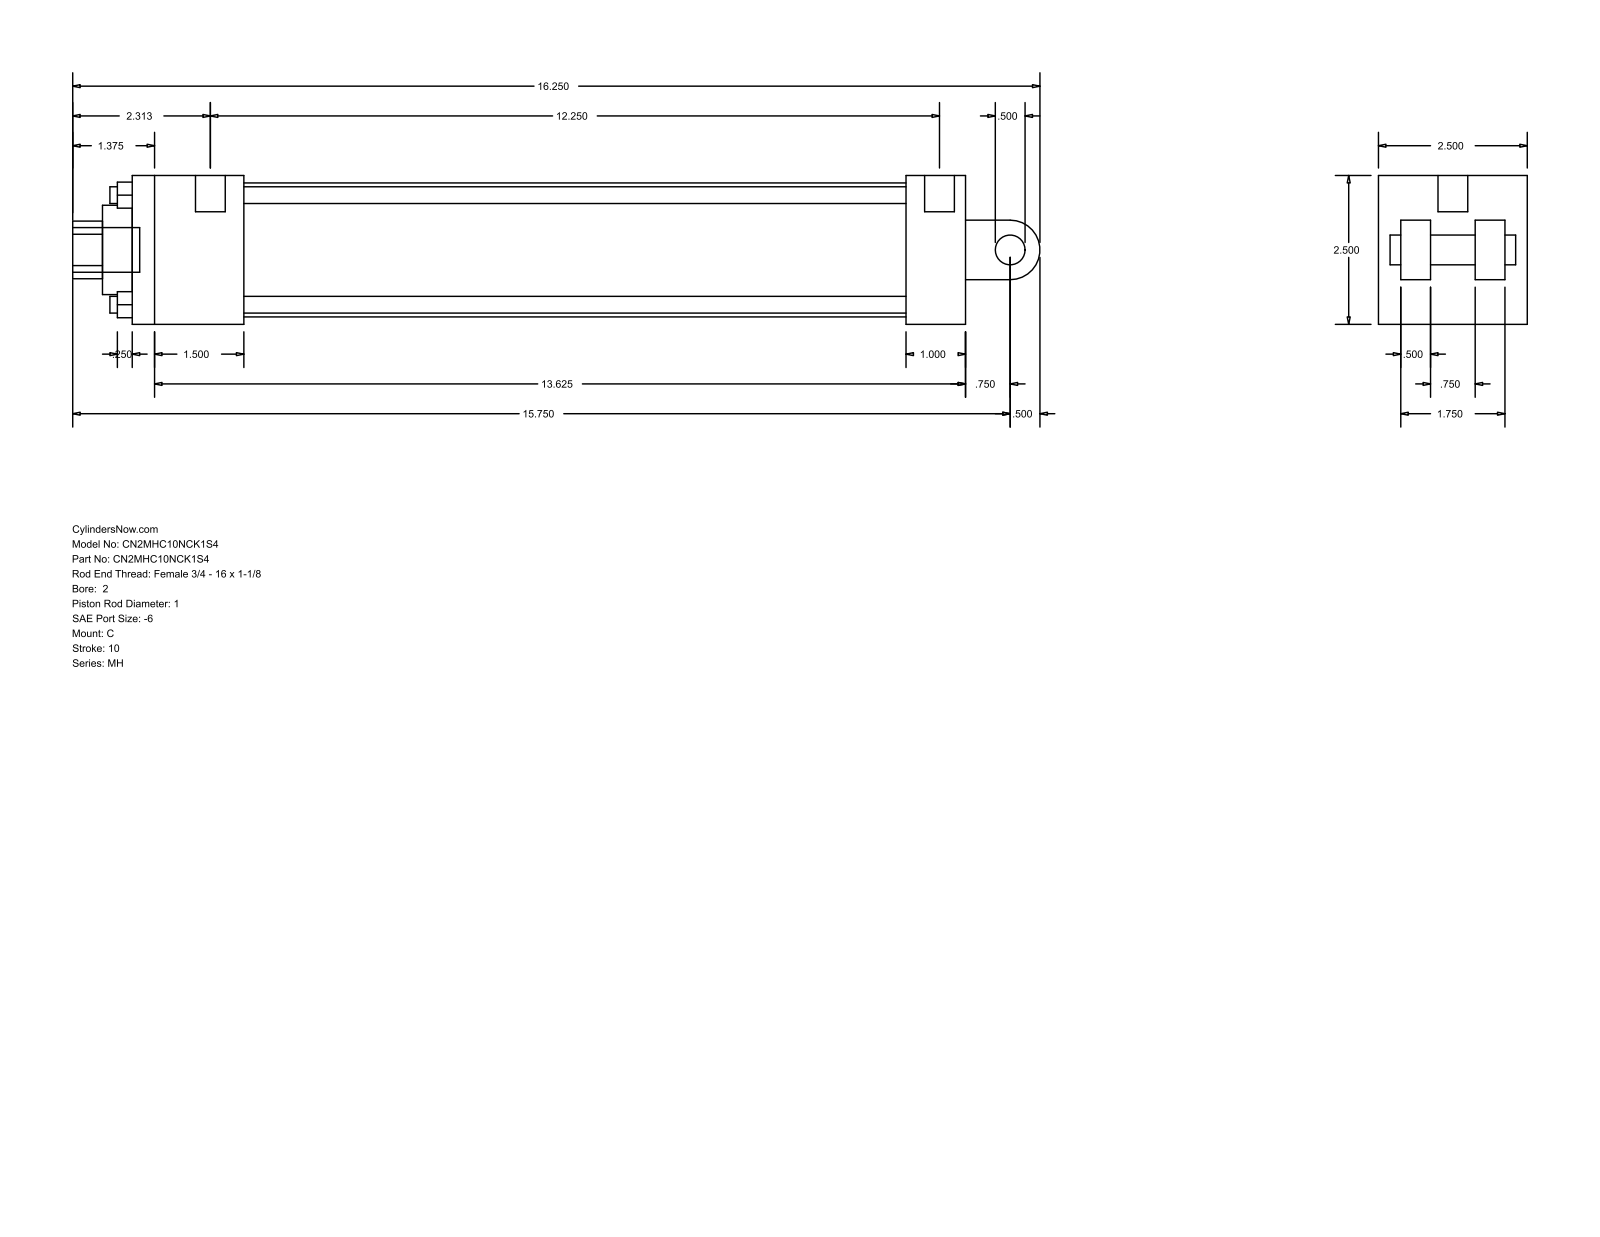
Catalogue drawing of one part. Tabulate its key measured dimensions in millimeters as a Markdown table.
| quantity | value |
| --- | --- |
| part name | MH_C__0200_1 |
| STEP written by | GSSL Pune (CONFIG_CONTROL_DESIGN) |
| units | millimeters |
| bodies | 0 solids, 99 faces (70 planar, 29 cylindrical, 0 other) |
| overall size | 412.75 × 63.5 × 63.5 |
| round holes (diameter × count) | 7.14 × 4, 5.56 × 2, 12.7 × 1, 25.4 × 1, 38.1 × 1, 57.15 × 1 |
| round bosses / shafts (diameter × count) | 12.7 × 2, 5.56 × 2, 19.05 × 1 |
| partial cylindrical surfaces (radius × count) | 12.29 × 1, 12.7 × 1 |
| main face-to-face distances | 63.5, 355.6, 12.7, 25.4, 9.52, 47.63, 53.98, 330.2, 282.57, 307.97 |
| hole center spacings | 33.05, 46.74, 66.1, 3.17 |
